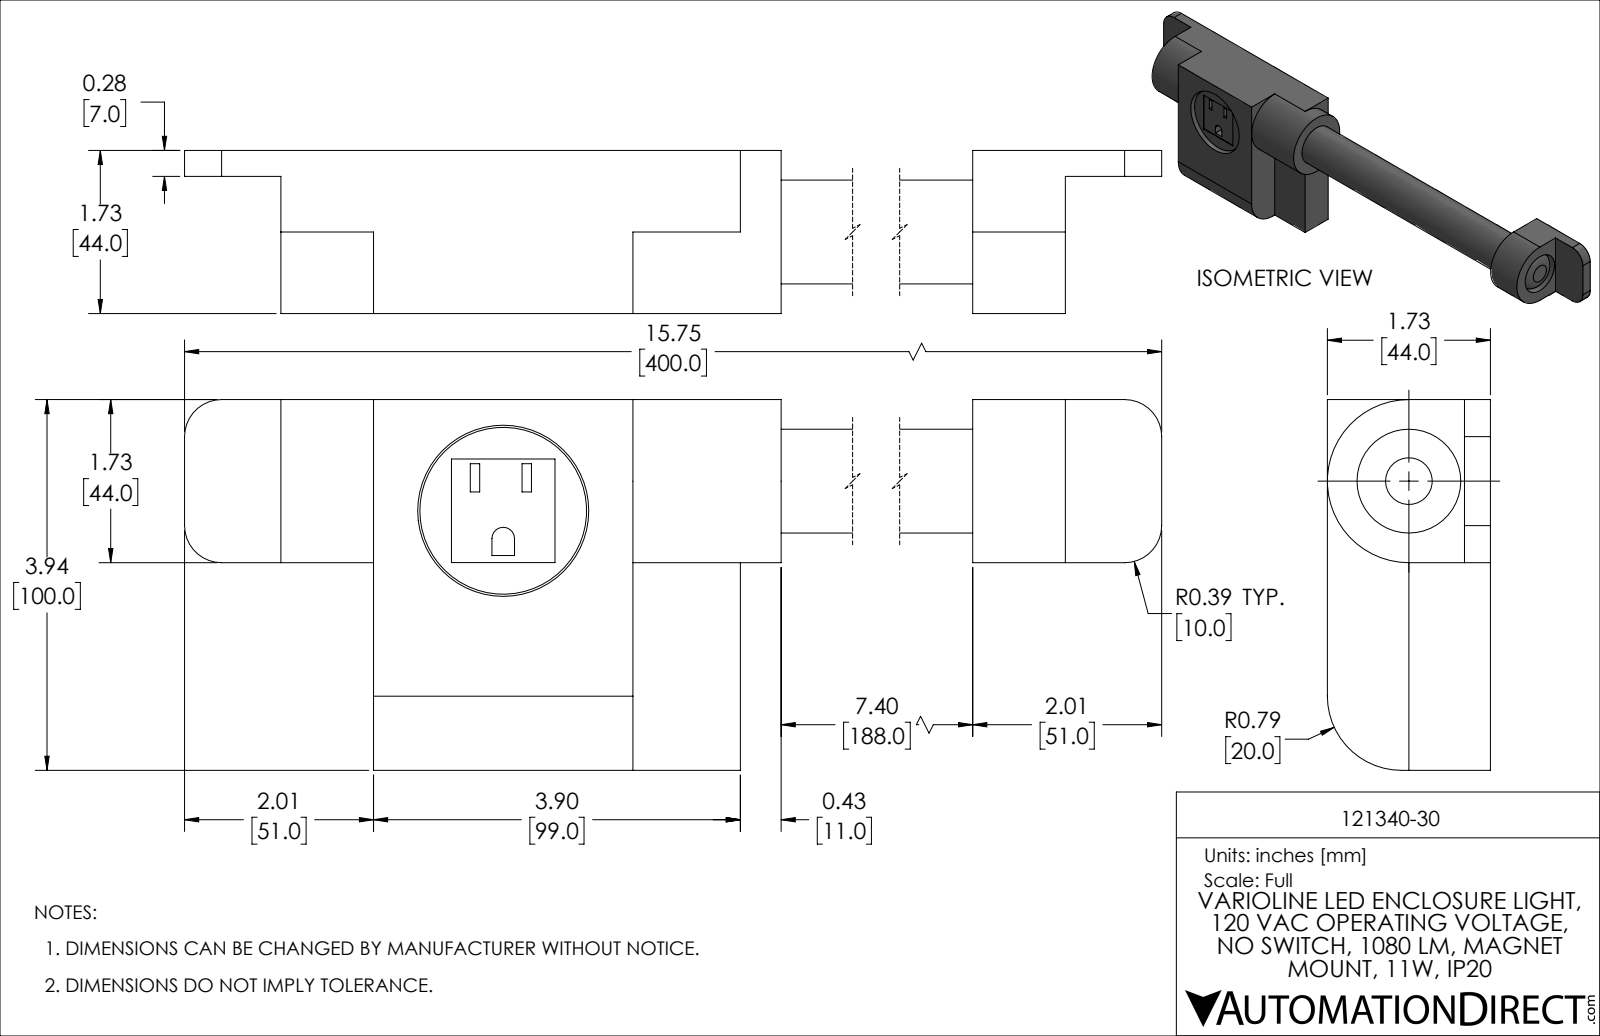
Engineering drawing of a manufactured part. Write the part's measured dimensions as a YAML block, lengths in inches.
part_name: "PRODUCT_NAME_1"
step_written_by: "ACIS (AUTOMOTIVE_DESIGN_CC2)"
units: inches
bodies: {solids: 1, faces: 75, planar: 47, cylindrical: 22, other: 6}
overall_size: [15.748, 3.937, 1.732]
volume: 37.32
surface_area: 123.4
round_holes:
  - {diameter: 1.102, count: 1}
  - {diameter: 1.817, count: 1}
round_bosses_or_shafts:
  - {diameter: 1.772, count: 1}
  - {diameter: 1.732, count: 1}
partial_cylinders:
  - {radius: 0.394, count: 4}
  - {radius: 0.12, count: 1}
  - {radius: 0.787, count: 1}
face_to_face_distances: [1.732, 0.866, 3.937, 0.276, 1.457, 0.984, 12.717, 0.591, 3.898, 2.756]
